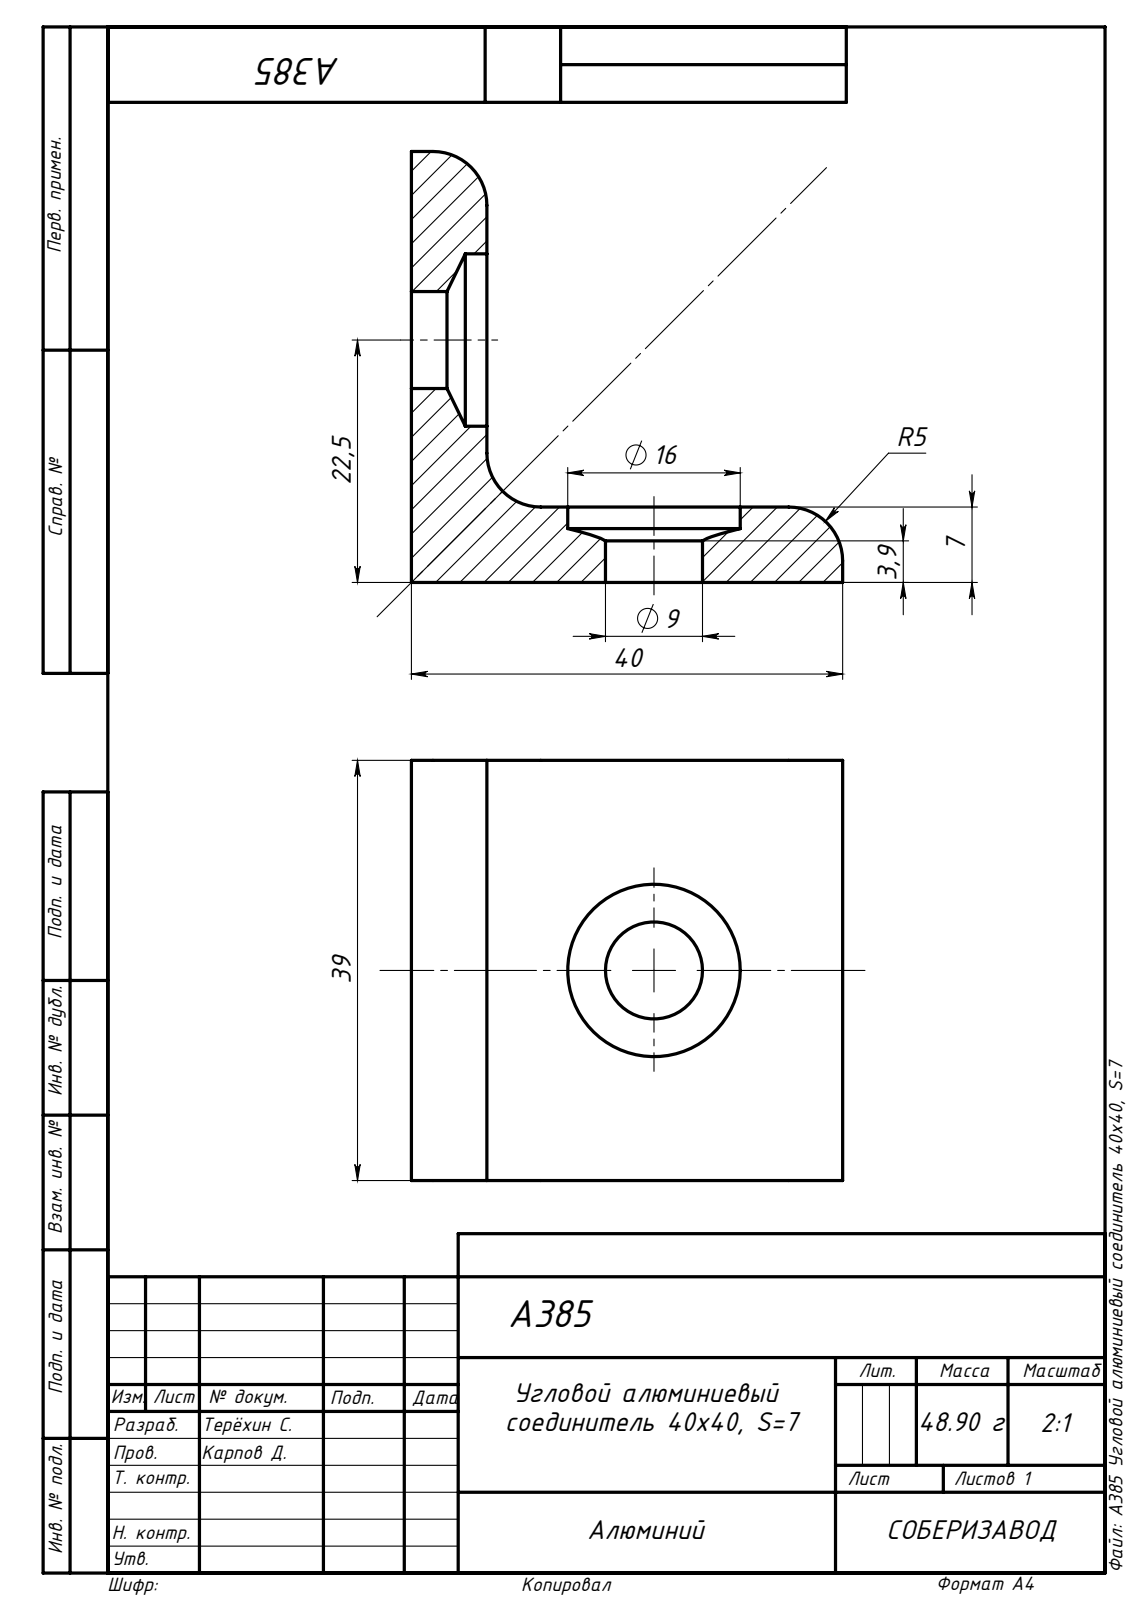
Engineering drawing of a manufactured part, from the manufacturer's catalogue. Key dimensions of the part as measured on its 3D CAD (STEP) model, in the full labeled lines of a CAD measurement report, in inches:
Part name (STEP PRODUCT): A385 Угловой алюминиевый соединитель 40х40, S=7
STEP written by: SolidWorks 2020 (AUTOMOTIVE_DESIGN)
Units: inches
Bodies: 1 solid, 23 faces (8 planar, 11 cylindrical, 4 other)
Overall size (bounding box): 1.575 × 1.575 × 1.535
Volume: 1.105 in³ · Surface area: 11.12 in²
Round holes (diameter × count): ⌀0.354 ×2, ⌀0.63 ×2
Partial cylindrical surfaces — rounded edges, fillets, slot ends (radius × count): R0.197 ×3
Main face-to-face distances: 0.276, 1.535, 1.575, 1.299
